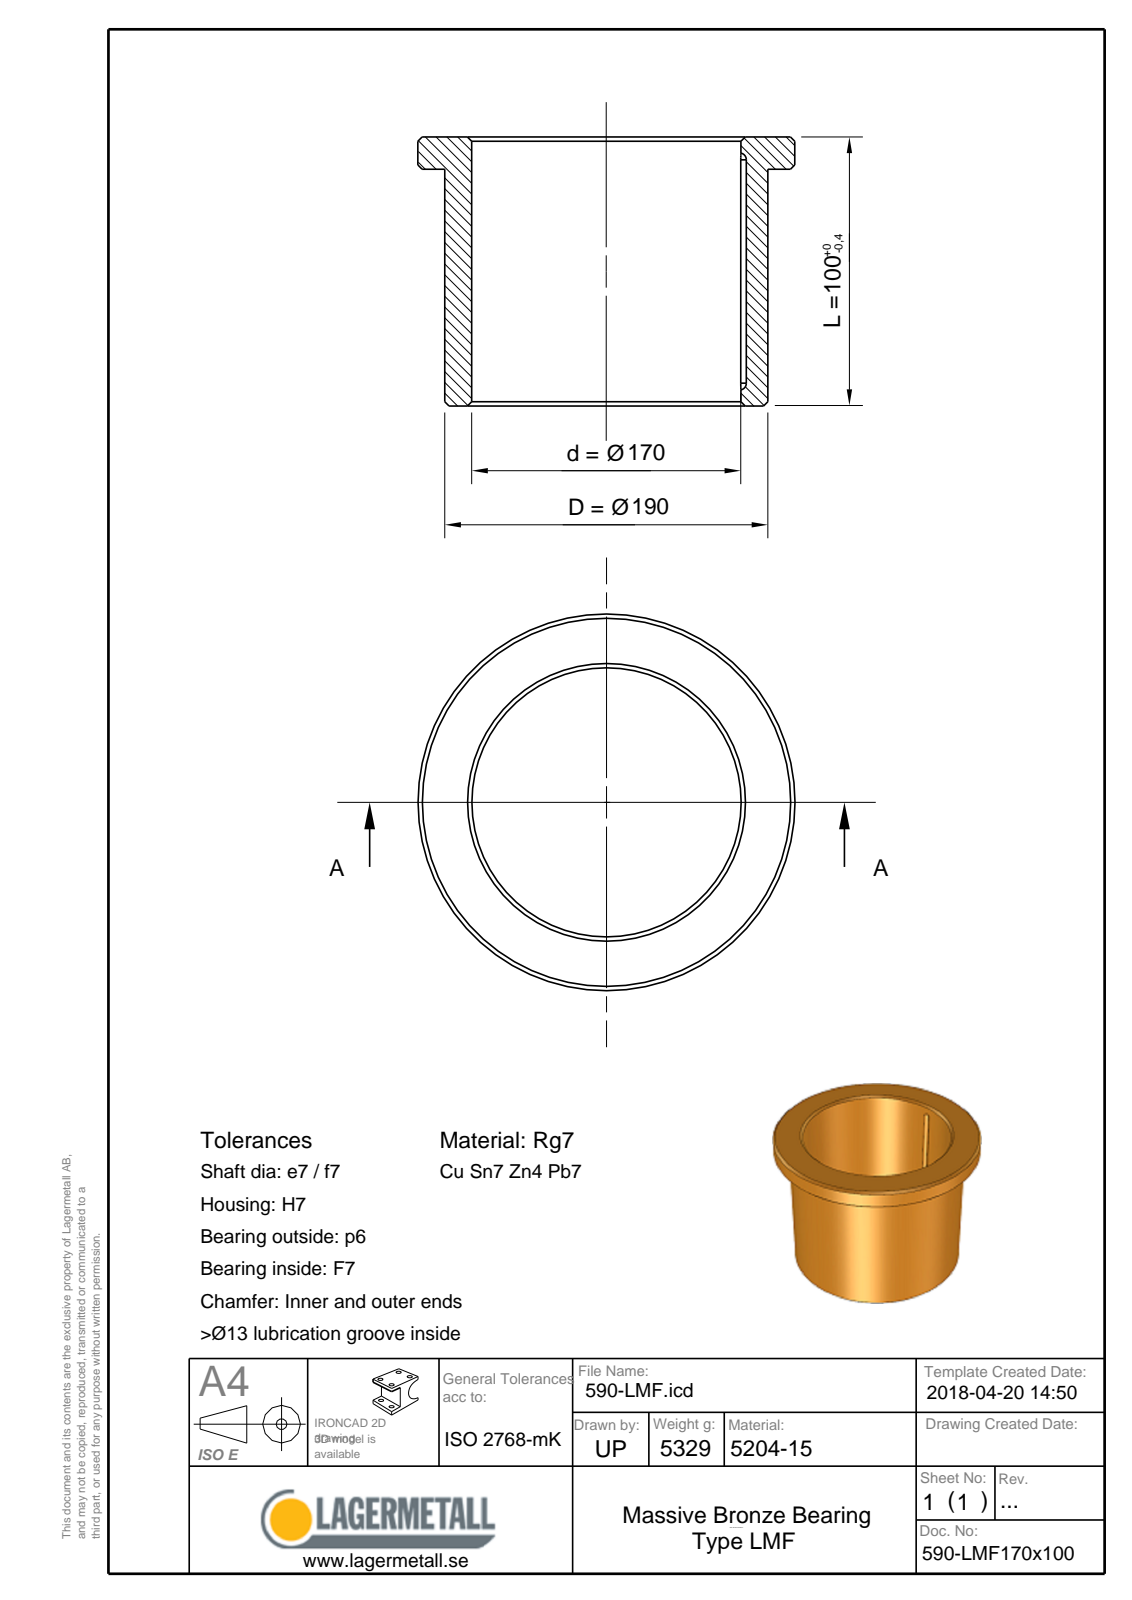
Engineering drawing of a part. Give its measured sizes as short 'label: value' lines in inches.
name: 590-LMF170x100
written by: Spatial InterOp 3D (CONFIG_CONTROL_DESIGN)
unit: in
bodies: 1 solid, 16 faces (4 planar, 5 cylindrical, 7 other)
size: 8.071 × 8.071 × 3.937
volume: 36.95 in³; area: 202.9 in²
holes: 1× ⌀6.693
bosses: 1× ⌀8.071, 1× ⌀7.48
rounds: 2× R0.089
face distances: 3.937, 3.543, 0.394
